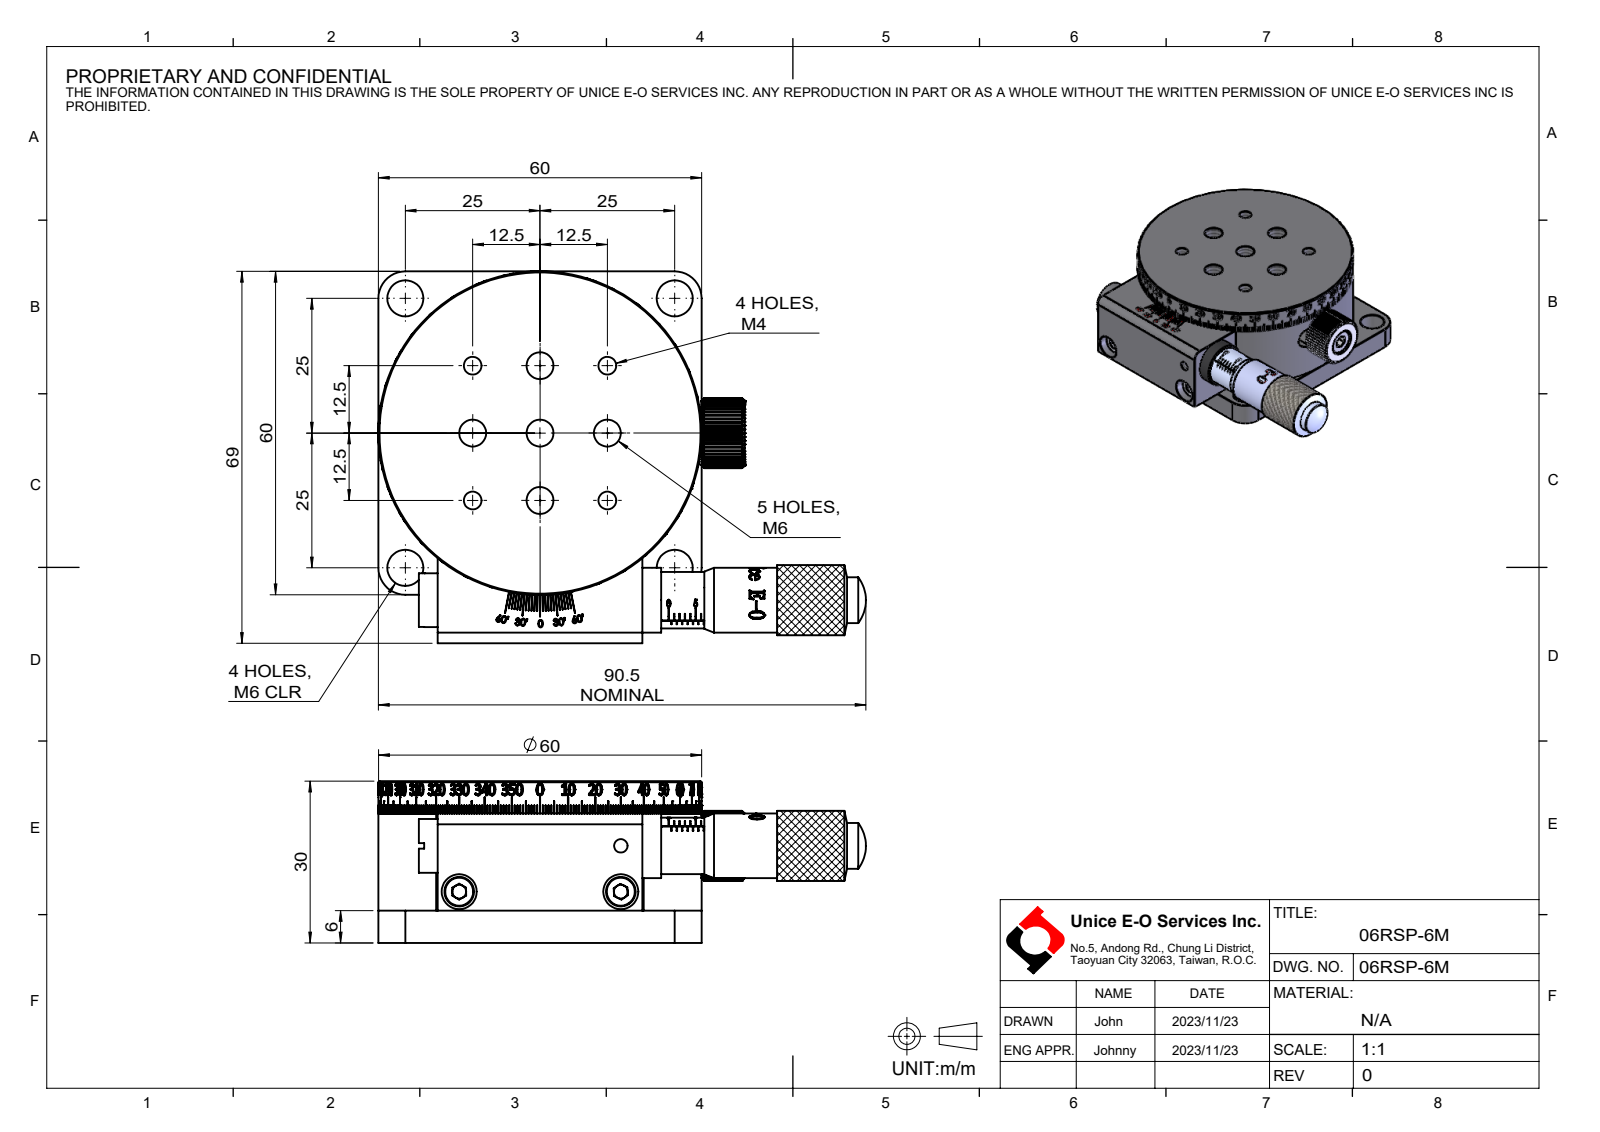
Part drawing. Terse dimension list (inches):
name: 06RSP-6M
written by: SolidWorks 2022 (CONFIG_CONTROL_DESIGN)
unit: in
bodies: 0 solids, 817 faces (367 planar, 255 cylindrical, 195 other)
size: 3.563 × 2.717 × 1.181
holes: 5× ⌀0.197, 4× ⌀0.13, 4× ⌀0.264, 2× ⌀0.256, 1× ⌀0.098, 1× ⌀0.26, 1× ⌀0.283, 1× ⌀0.417, 1× ⌀1.22
bosses: 1× ⌀2.362, 1× ⌀1.181, 1× ⌀0.512, 1× ⌀0.472, 1× ⌀0.413, 1× ⌀0.394, 1× ⌀0.335, 1× ⌀0.157
rounds: 4× R0.197, 2× R0.118, 1× R0.079, 1× R0.235, 1× R0.256, 1× R1.181
face distances: 0.236, 0.945, 1.181, 0.709, 0.079, 0.157, 0.787, 1.024, 2.362, 0.15
hole spacings: 1.1, 0.492, 0.696, 1.556, 1.774, 0.984, 1.392, 1.969
